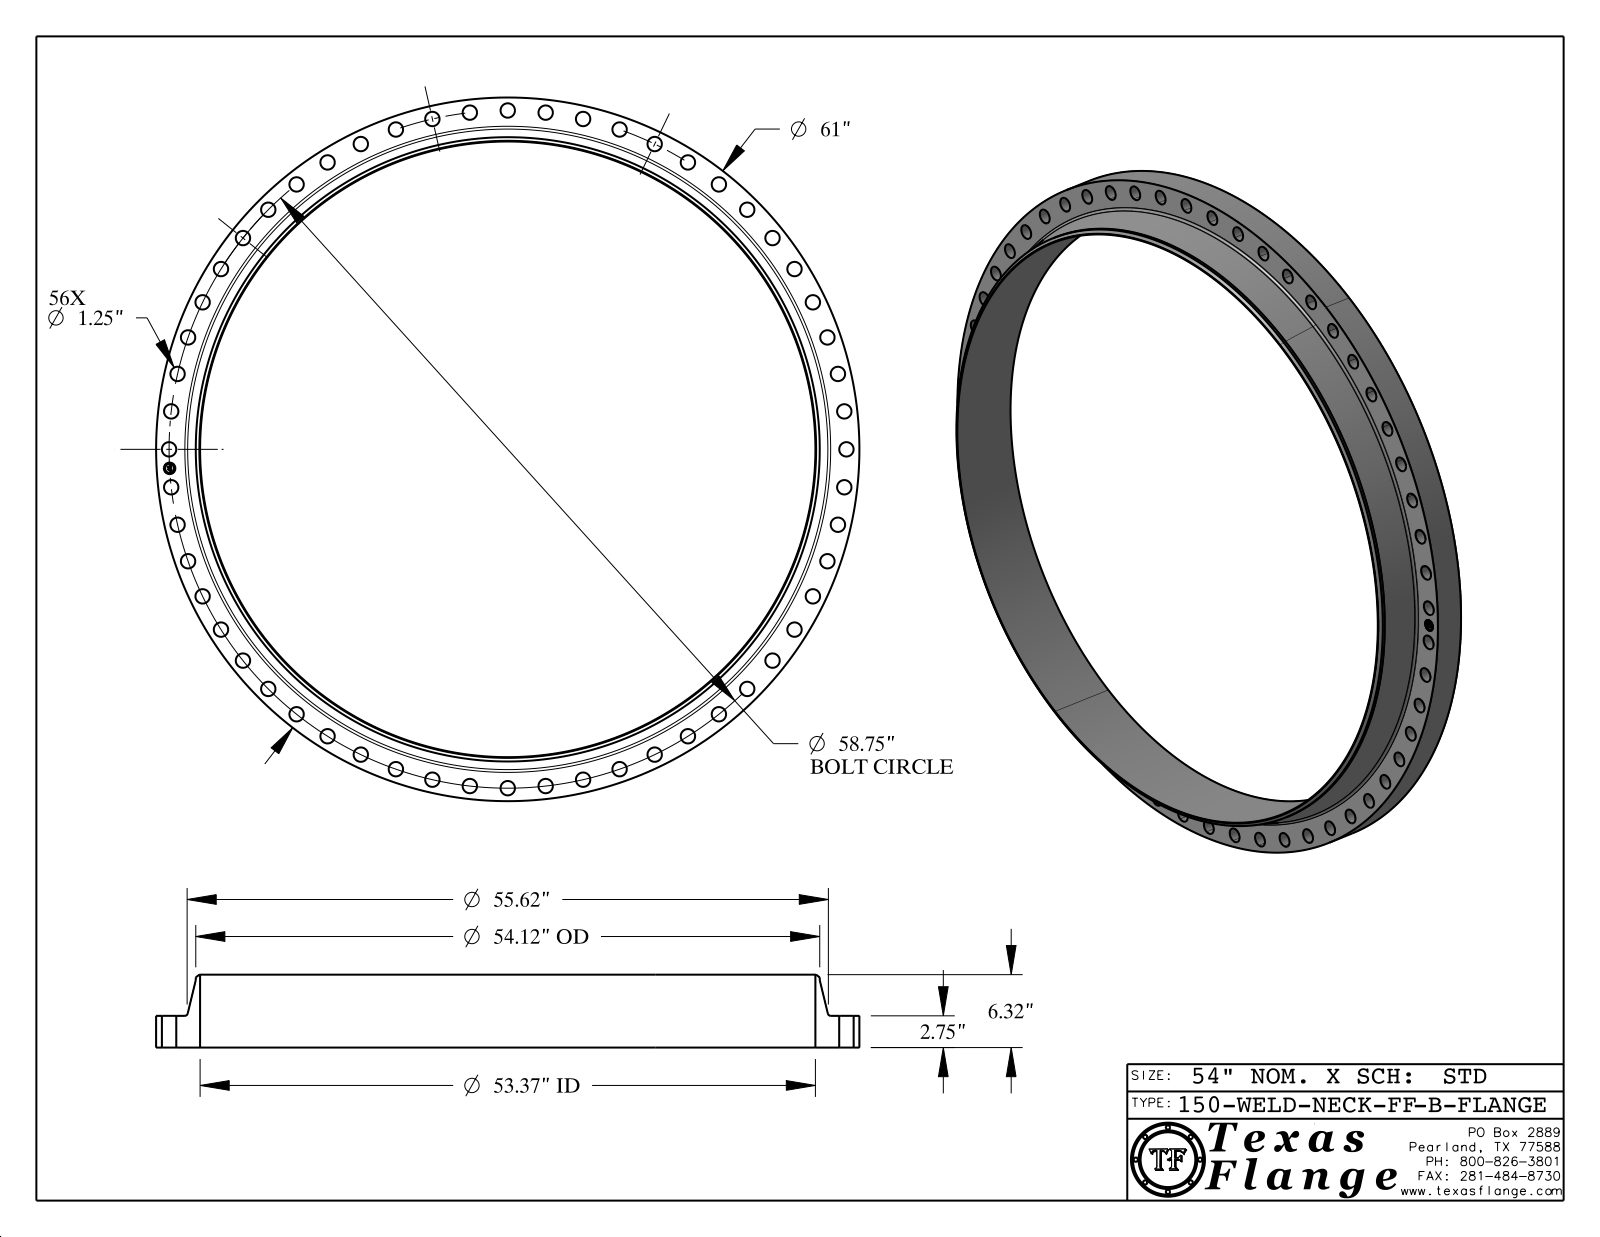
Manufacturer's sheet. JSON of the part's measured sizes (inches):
{"part_name": "150-WELD-NECK-FF, Series B", "step_written_by": "CATIA V5 STEP AP214 (AUTOMOTIVE_DESIGN)", "units": "inches", "bodies": {"solids": 1, "faces": 512, "planar": 368, "cylindrical": 138, "other": 6}, "overall_size": [61, 61, 6.32], "volume_in3": 2116, "surface_area_in2": 3888, "round_holes": [[1.25, 56], [1, 1], [53.37, 1]], "round_bosses_or_shafts": [[0.061, 8], [61, 1], [54.12, 1], [0.788, 1]], "face_to_face_distances": [2.75, 6.32, 3.57, 0.015, 2.735, 3.585, 0.298, 0.292, 0.019, 0.054], "hole_center_spacings": [58.657, 3.294, 6.578, 9.841, 29.375, 16.264, 19.404, 13.073]}
